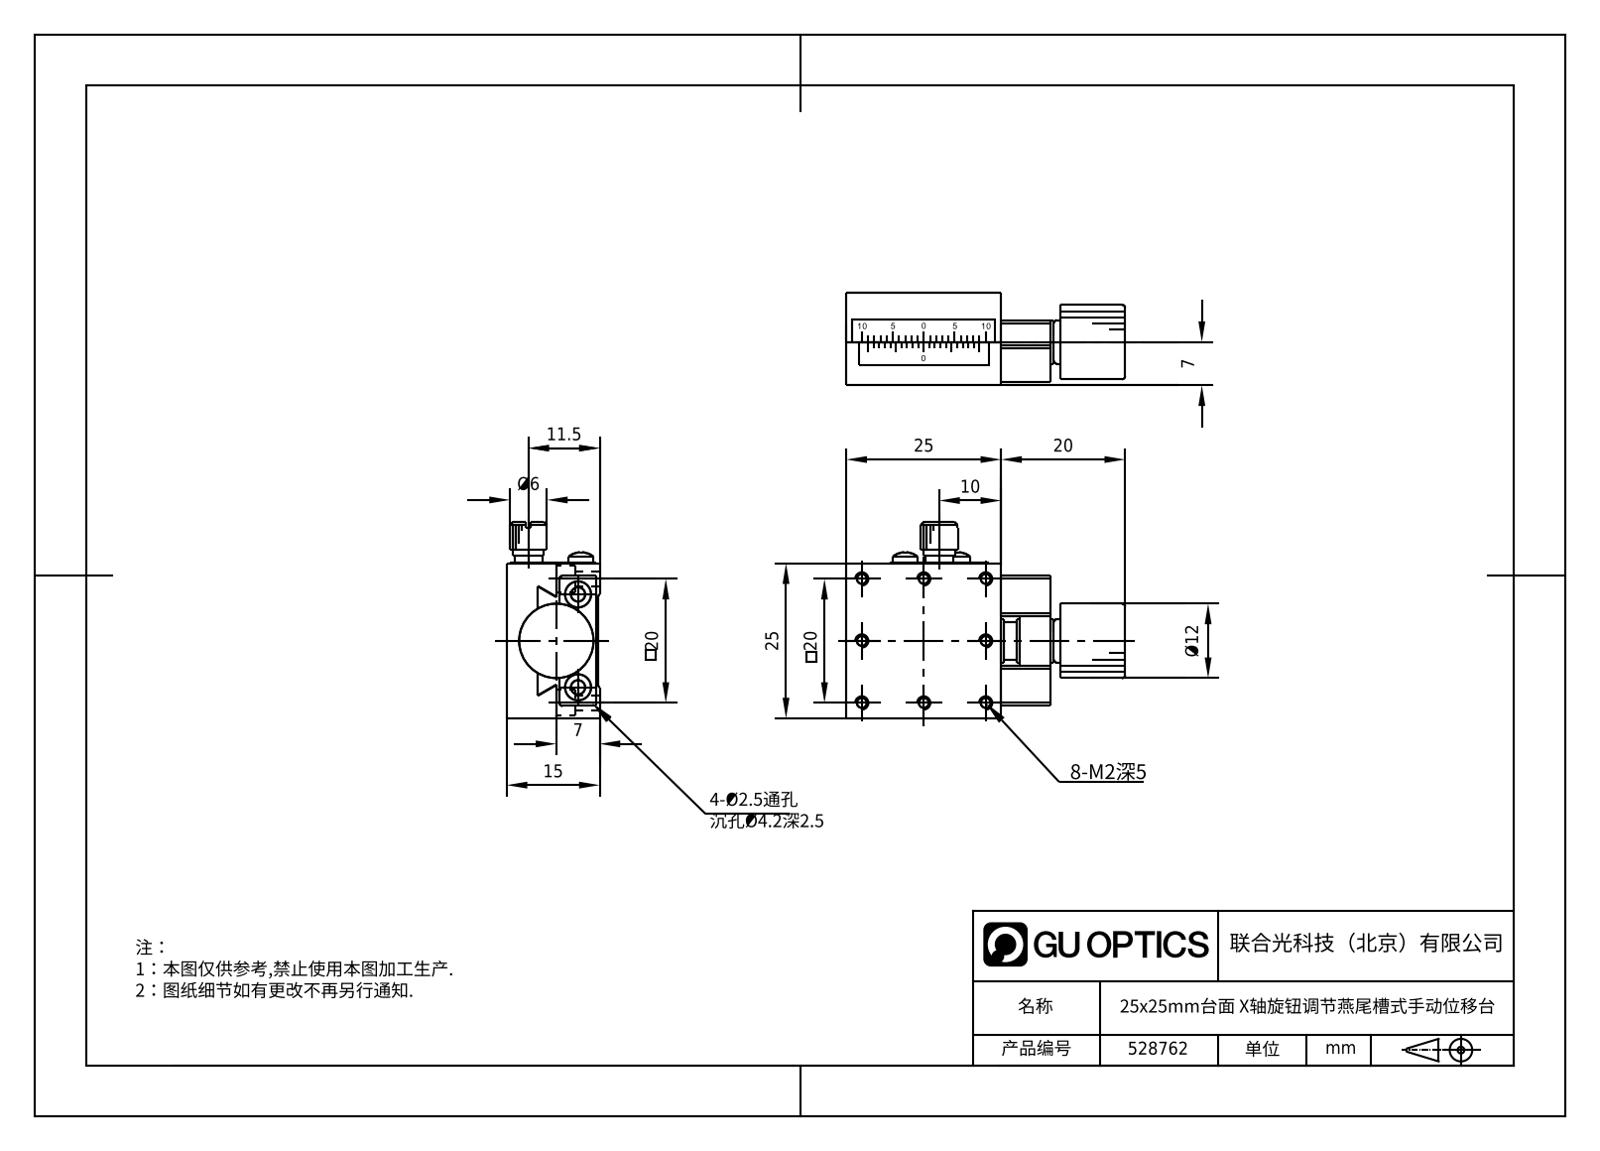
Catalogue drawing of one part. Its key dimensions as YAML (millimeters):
part_name: "528762"
step_written_by: "SolidWorks 2020 (CONFIG_CONTROL_DESIGN)"
units: millimeters
bodies: {solids: 3, faces: 476, planar: 205, cylindrical: 118, other: 153}
overall_size: [45, 33.56, 15]
volume: 10106
surface_area: 8676
round_holes:
  - {diameter: 1.57, count: 12}
  - {diameter: 2.5, count: 10}
  - {diameter: 4, count: 5}
  - {diameter: 1.57, count: 4}
  - {diameter: 4.2, count: 4}
  - {diameter: 2.01, count: 3}
  - {diameter: 2.2, count: 2}
  - {diameter: 2.01, count: 1}
  - {diameter: 2.46, count: 1}
  - {diameter: 7, count: 1}
round_bosses_or_shafts:
  - {diameter: 6, count: 2}
  - {diameter: 4, count: 1}
  - {diameter: 3, count: 1}
  - {diameter: 2, count: 1}
partial_cylinders:
  - {radius: 1, count: 8}
  - {radius: 1.25, count: 2}
  - {radius: 6, count: 1}
face_to_face_distances: [4, 8, 0.5, 7, 15, 4.5, 2.5, 10.5, 3.5, 11]
hole_center_spacings: [10, 22.36, 20, 10.44, 12.21, 14.14, 16.4, 7]
